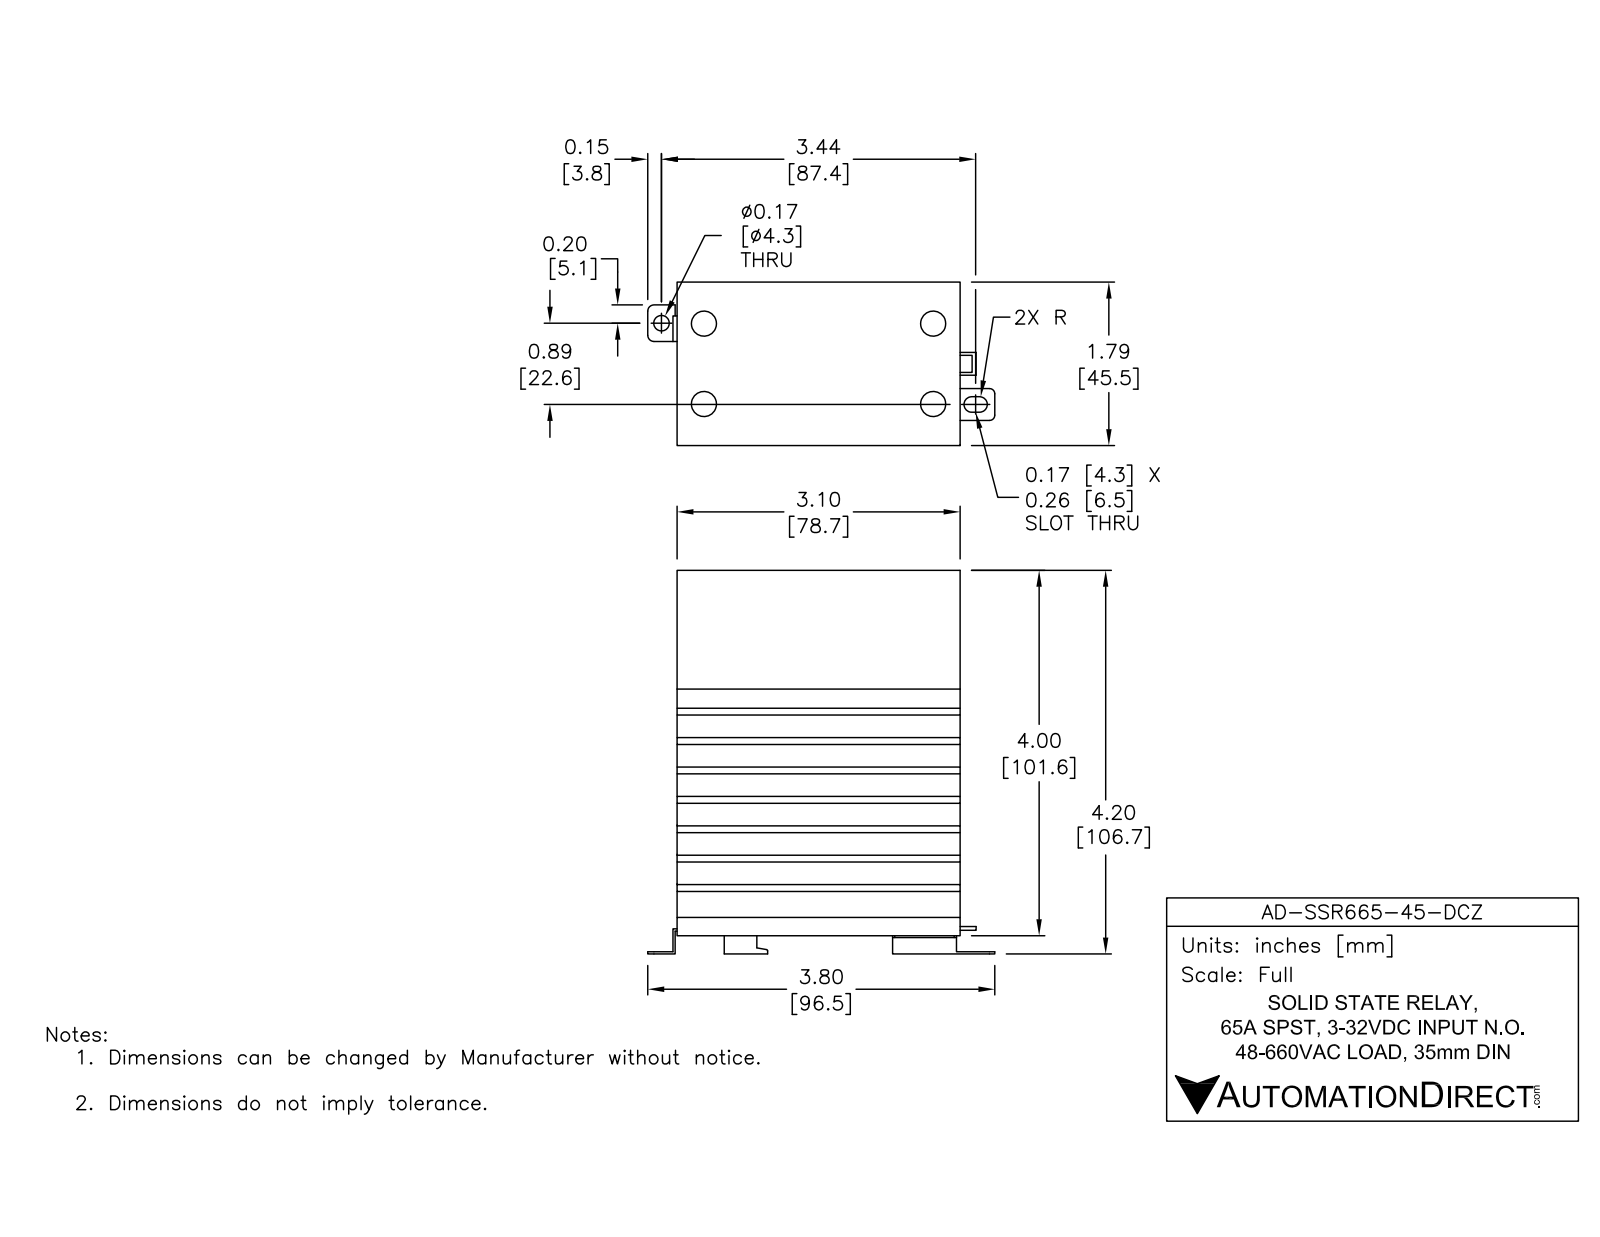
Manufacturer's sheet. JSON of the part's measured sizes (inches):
{"part_name": "AD-SSR665-45-DCZ", "step_written_by": "SolidWorks 2014 (AUTOMOTIVE_DESIGN)", "units": "inches", "bodies": {"solids": 1, "faces": 171, "planar": 151, "cylindrical": 20, "other": 0}, "overall_size": [4.2, 3.8, 1.79], "volume_in3": 12.46, "surface_area_in2": 125.1, "round_holes": [[0.275, 2], [0.275, 2], [0.17, 1]], "partial_cylinders_radius": [[0.05, 2], [0.058, 2], [0.067, 2], [0.085, 2], [0.015, 1]], "face_to_face_distances": [0.644, 0.322, 0.966, 0.397, 0.322, 0.247, 1.609, 0.075, 0.569, 0.075], "hole_center_spacings": [0.88, 2.51, 2.66, 0.465, 1, 2.975, 3.104]}
